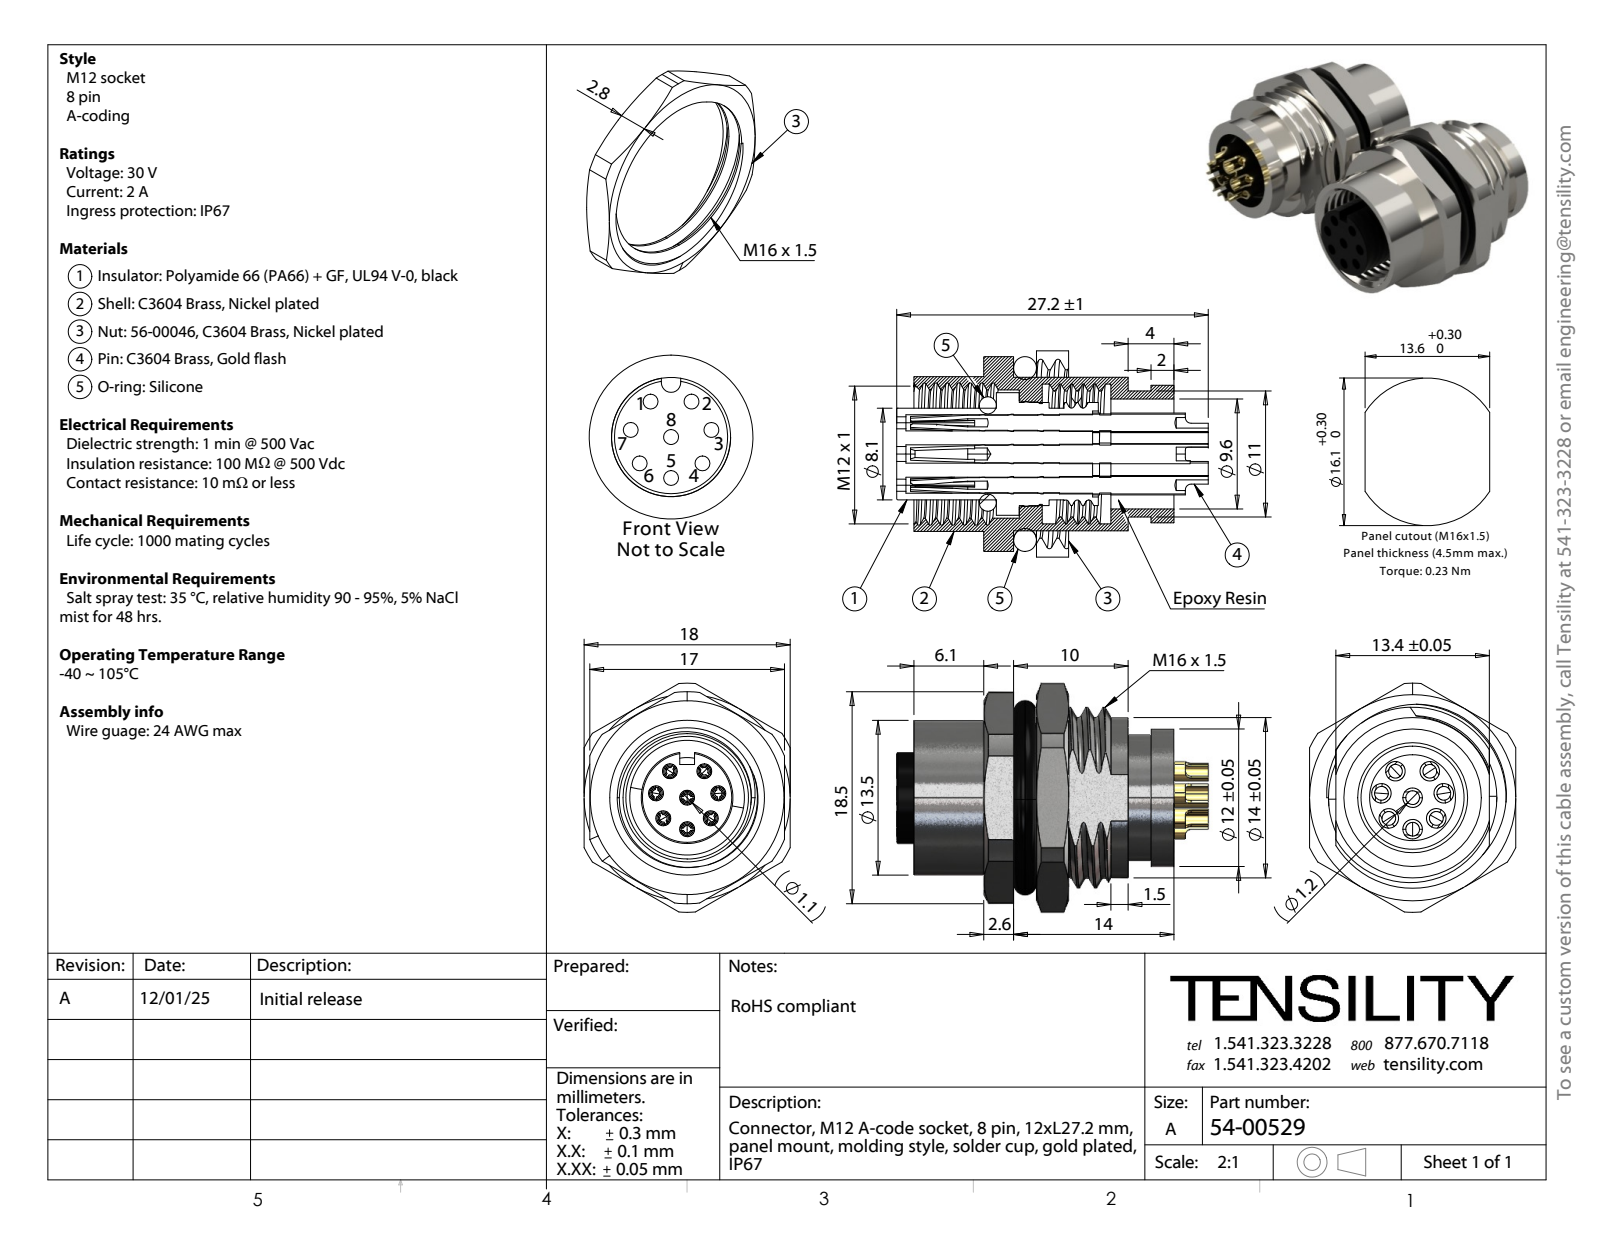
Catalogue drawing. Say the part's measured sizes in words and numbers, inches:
The part is named "56-00046; 10-7-15000_1.STEP; 54-00529". Its 3-D file was written by "SolidWorks 2025 (CONFIG_CONTROL_DESIGN)". It is 13 solids with 763 faces: 195 planar, 310 cylindrical and 258 other. Overall it measures 1.071 by 0.787 by 0.709 inches. Its volume is 0.174 cubic inches and its surface area 9.779 square inches. Round holes: 8 of diameter 0.047, 8 of diameter 0.051, 8 of diameter 0.063, 1 of diameter 0.295, 1 of diameter 0.346, 1 of diameter 0.358, 1 of diameter 0.378, 1 of diameter 0.441, 1 of diameter 0.48, 1 of diameter 0.579. Round bosses or shafts: 8 of diameter 0.067, 8 of diameter 0.061, 8 of diameter 0.06, 1 of diameter 0.551, 1 of diameter 0.549, 1 of diameter 0.531, 1 of diameter 0.472, 1 of diameter 0.433. Partial cylindrical surfaces (rounded edges, fillets, slot ends): 8 of radius 0.02, 1 of radius 0.311, 1 of radius 0.364, 1 of radius 0.394. The main face-to-face distances are 0.02, 0.079, 0.059, 0.102, 0.394, 0.689, 0.315, 0.374, 0.091, 0.453. The hole center spacings are 0.108, 0.163, 0.09, 0.207, 0.089, 0.183, 0.214, 0.09.
